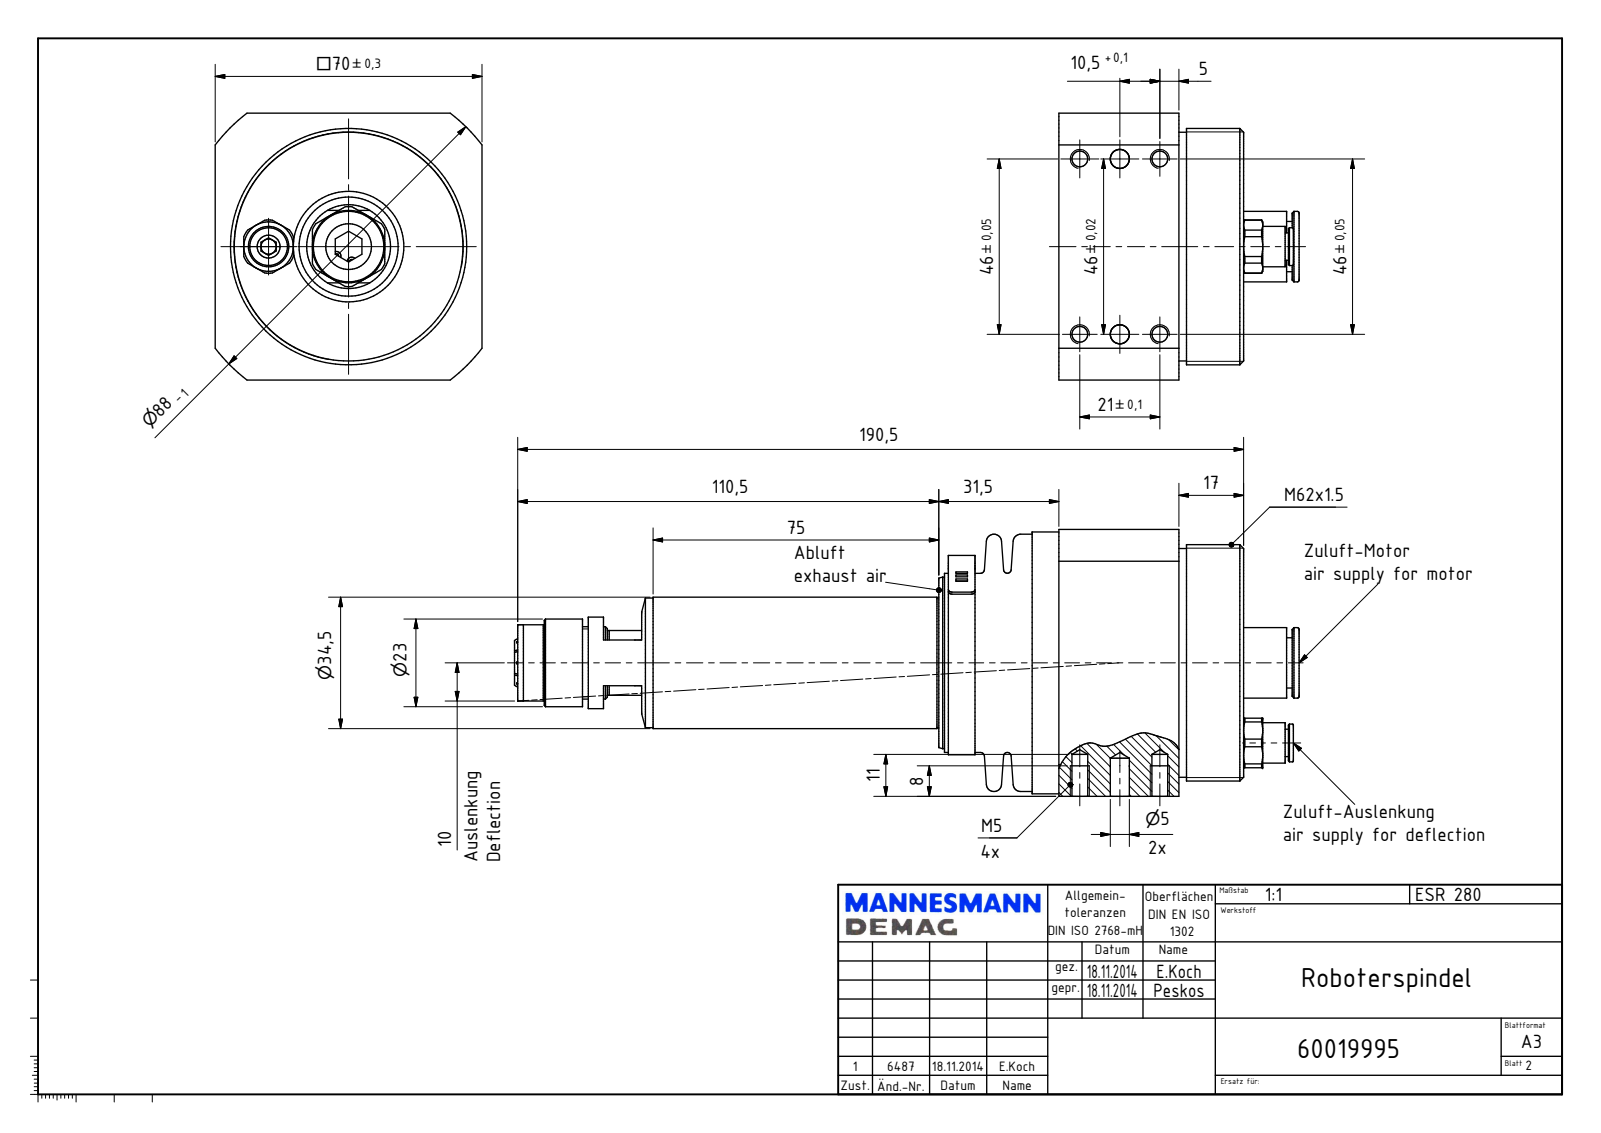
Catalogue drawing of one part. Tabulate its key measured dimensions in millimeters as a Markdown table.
| quantity | value |
| --- | --- |
| part name | ESR 280_60019995 |
| STEP written by | Autodesk Inventor 2018 (AUTOMOTIVE_DESIGN) |
| units | millimeters |
| bodies | 1 solid, 459 faces (188 planar, 149 cylindrical, 122 other) |
| overall size | 205.92 × 70 × 70 |
| volume | 362 024 mm³ |
| surface area | 57 162 mm² |
| round holes (diameter × count) | 4.13 × 4, 4.99 × 2, 5 × 2, 6 × 2, 4 × 1, 8.57 × 1, 11 × 1, 12 × 1, 12.2 × 1, 13.2 × 1, 17.92 × 1, 29 × 1 |
| round bosses / shafts (diameter × count) | 68.7 × 1, 67.5 × 1, 62 × 1, 60 × 1, 48.83 × 1, 48.2 × 1, 47 × 1, 45.85 × 1 |
| partial cylindrical surfaces (radius × count) | 0.5 × 8, 1 × 8, 1.1 × 8, 18.09 × 6, 33.72 × 6, 1.4 × 4, 2 × 4, 7 × 1 |
| main face-to-face distances | 70, 17, 31.5, 0.5, 48.5, 34.75, 35.25, 63, 80, 9.75 |
| hole center spacings | 10.5, 47.18, 21, 46, 50.57 |
